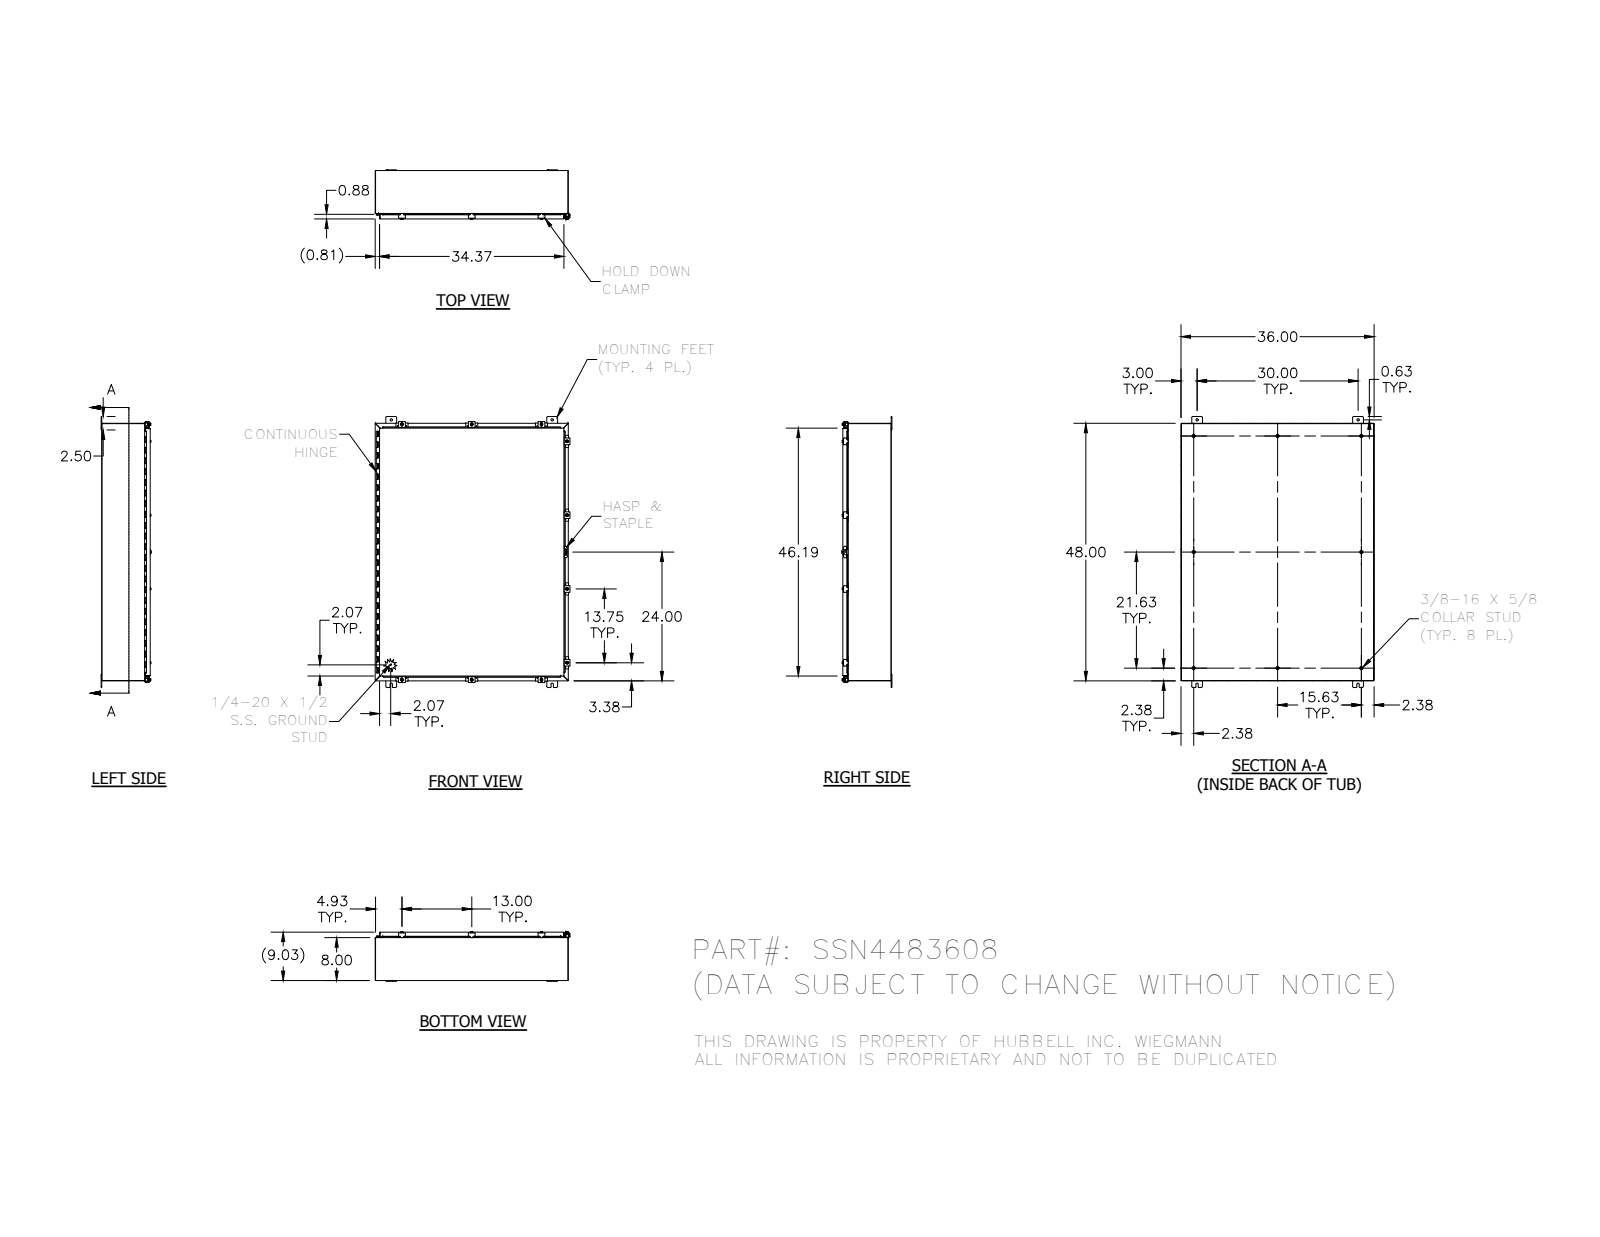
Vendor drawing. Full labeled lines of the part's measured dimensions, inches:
Part name (STEP PRODUCT): 38859; SSN4483608BTB; SSN4483608; HFW30825-3 (+8 more)
STEP written by: SolidWorks 2014 (AUTOMOTIVE_DESIGN)
Units: inches
Bodies: 73 solids, 2902 faces (1139 planar, 1258 cylindrical, 505 other)
Overall size (bounding box): 50.5 × 36.311 × 9.355
Volume: 413.4 in³ · Surface area: 10 950 in²
Round holes (diameter × count): ⌀0.11 ×23, ⌀0.211 ×10, ⌀0.281 ×10, ⌀0.3 ×10, ⌀0.438 ×4, ⌀0.125 ×1, ⌀0.156 ×1, ⌀0.5 ×1
Round bosses / shafts (diameter × count): ⌀0.25 ×12, ⌀0.52 ×10, ⌀0.5 ×10, ⌀0.35 ×10, ⌀0.625 ×8, ⌀0.33 ×8, ⌀0.337 ×1, ⌀0.12 ×1
Partial cylindrical surfaces — rounded edges, fillets, slot ends (radius × count): R0.03 ×117, R0.125 ×41, R0.25 ×37, R0.031 ×21, R0.105 ×21, R0.141 ×20, R0.062 ×18, R0.1 ×14
Main face-to-face distances: 0.074, 8.959, 8.885, 9.033, 35.926, 47.926, 7.926, 1.033, 35.852, 36
Hole centre spacings: 0.876, 13, 47.296, 12.192, 13.817, 48.727, 48.834, 49.265
